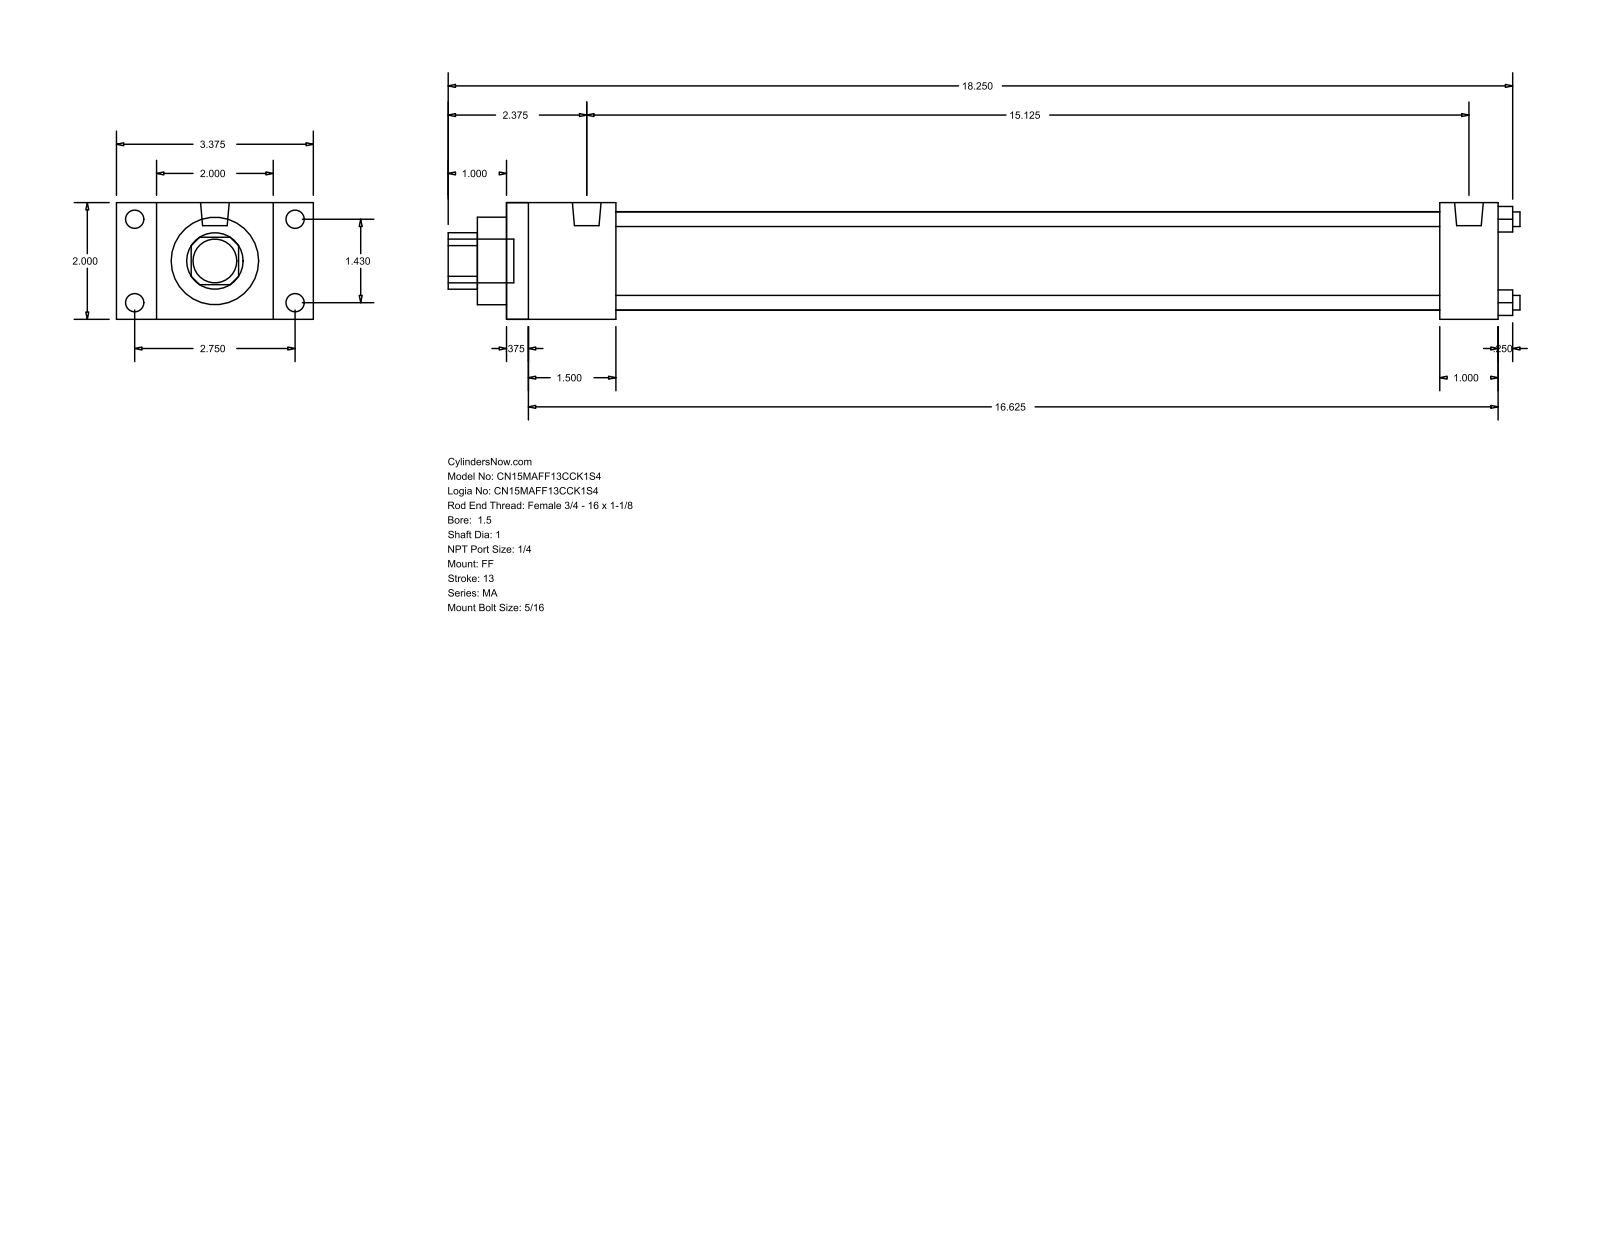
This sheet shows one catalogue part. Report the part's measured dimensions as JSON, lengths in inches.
{"part_name": "MA_FF__0150_1", "step_written_by": "GSSL Pune (CONFIG_CONTROL_DESIGN)", "units": "inches", "bodies": {"solids": 0, "faces": 92, "planar": 64, "cylindrical": 28, "other": 0}, "overall_size": [18.375, 3.375, 2], "round_holes": [[0.25, 4], [1, 1], [1.5, 1], [1.69, 1]], "round_bosses_or_shafts": [[0.313, 8], [0.492, 2], [0.75, 1]], "partial_cylinders_radius": [[0.484, 1]], "face_to_face_distances": [2, 17, 0.375, 16.625, 1, 1.875, 16, 1.5, 15.625, 14.125], "hole_center_spacings": [1.011, 1.43, 2.022]}
